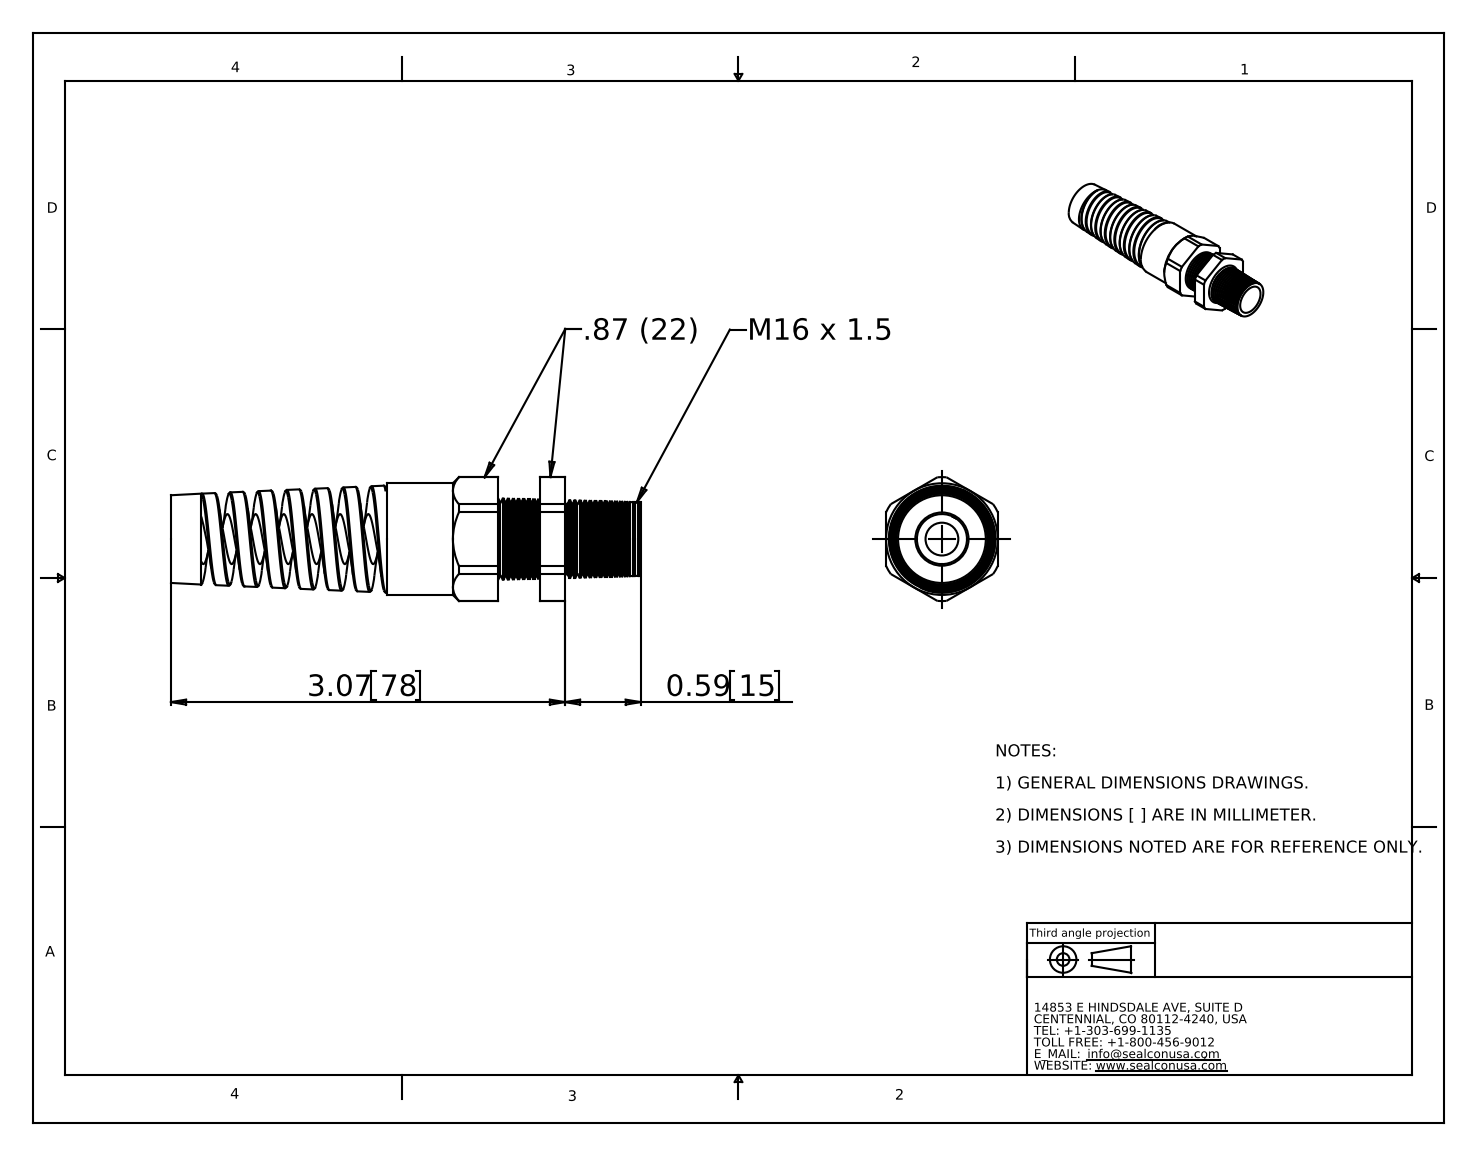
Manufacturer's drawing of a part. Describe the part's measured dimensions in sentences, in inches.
The part is named "CF17DR-BK". Its 3-D file was written by "SolidWorks 2008 (CONFIG_CONTROL_DESIGN)". It is 2 solids with 239 faces: 25 planar, 39 cylindrical and 175 other. Overall it measures 3.66 by 0.966 by 0.87 inches. Its volume is 1.017 cubic inches and its surface area 19.3 square inches. Round holes: 1 of diameter 0.256, 1 of diameter 0.39, 1 of diameter 0.415. Round bosses or shafts: 1 of diameter 0.87, 1 of diameter 0.635. Partial cylindrical surfaces (rounded edges, fillets, slot ends): 1 of radius 0.483. The main face-to-face distances are 0.87, 0.323, 0.52, 0.197, 0.354, 0.677, 0.874, 2.196, 2.55, 2.873.
